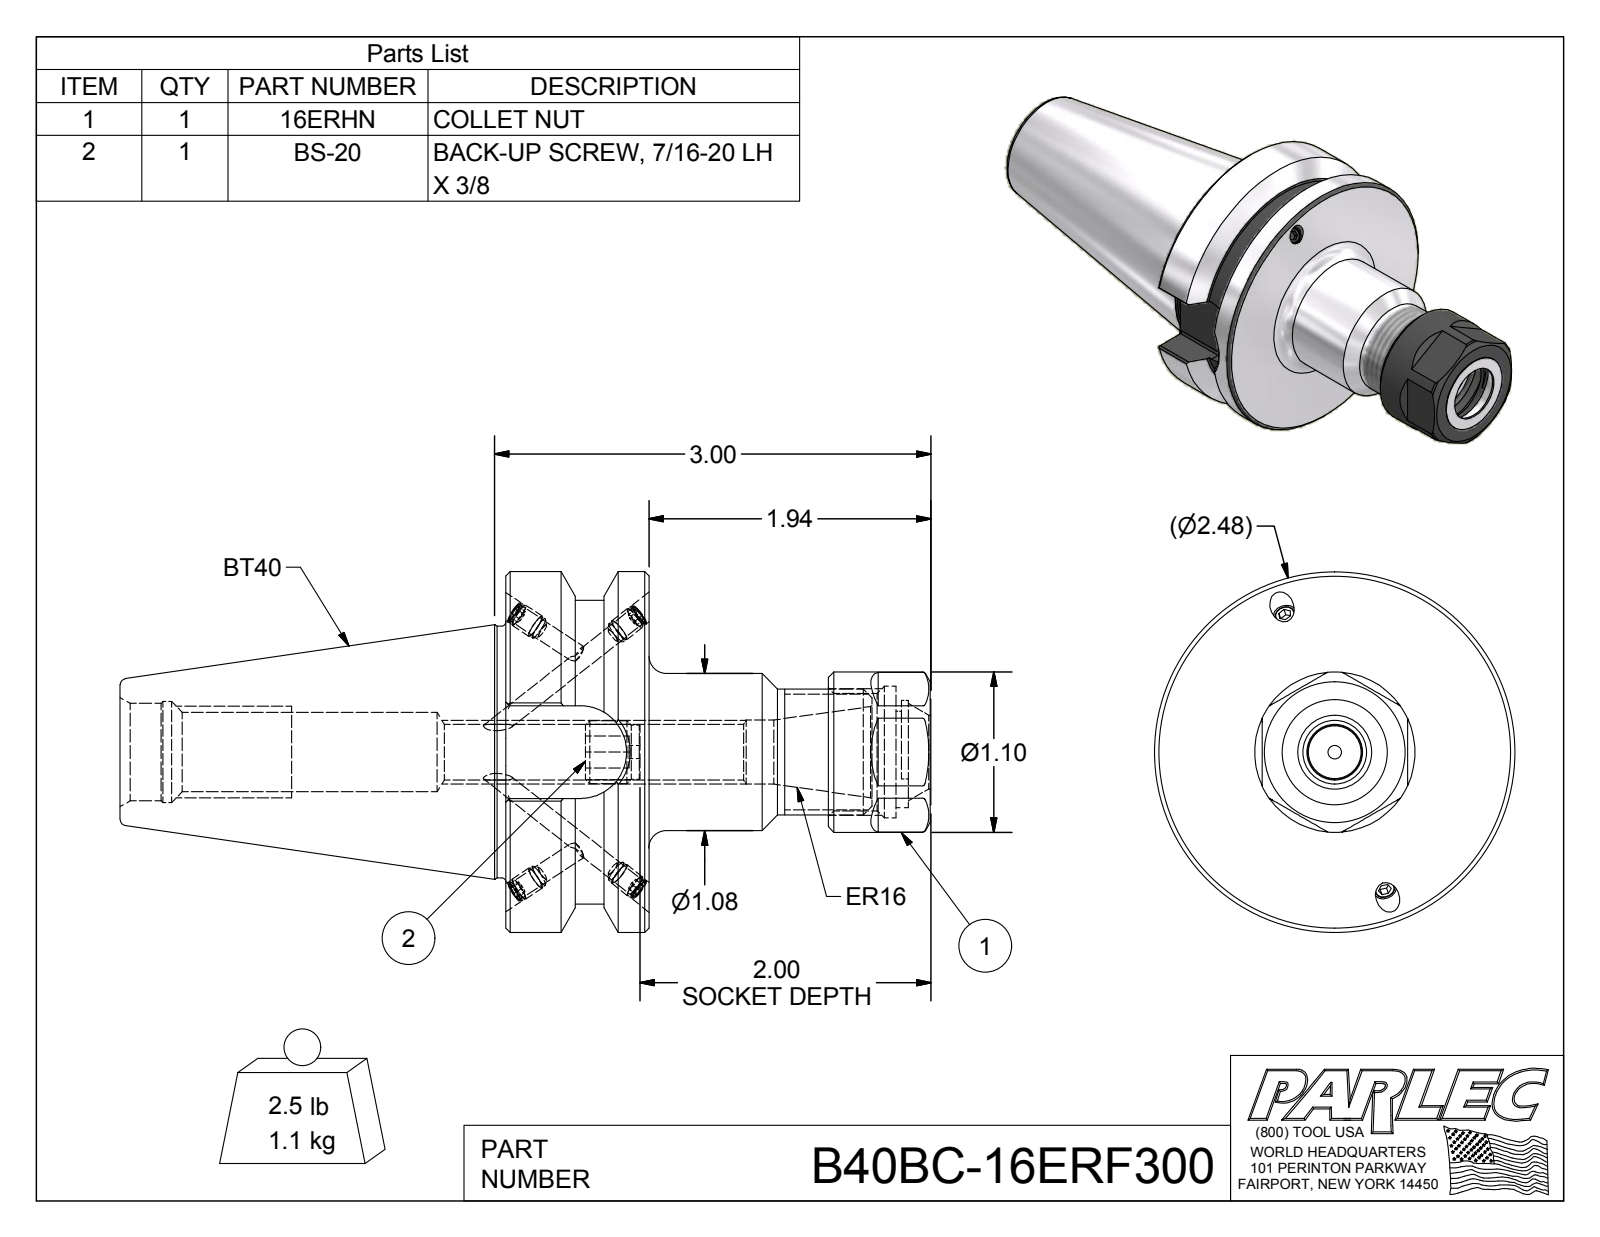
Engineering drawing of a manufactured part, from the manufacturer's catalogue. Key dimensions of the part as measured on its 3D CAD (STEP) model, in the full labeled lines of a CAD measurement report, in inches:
Part name (STEP PRODUCT): B40BCB-16ER3-1; 029-965; 16ERHN; BS-20 (+1 more)
STEP written by: Autodesk Inventor 2016 (AUTOMOTIVE_DESIGN)
Units: inches
Bodies: 7 solids, 201 faces (93 planar, 53 cylindrical, 55 other)
Overall size (bounding box): 5.575 × 2.48 × 2.48
Volume: 8.666 in³ · Surface area: 48.95 in²
Round holes (diameter × count): ⌀0.13 ×4, ⌀0.161 ×4, ⌀0.09 ×1, ⌀0.383 ×1, ⌀0.44 ×1, ⌀0.488 ×1, ⌀0.545 ×1, ⌀0.67 ×1, ⌀0.67 ×1, ⌀0.694 ×1, ⌀0.807 ×1, ⌀0.906 ×1
Round bosses / shafts (diameter × count): ⌀0.165 ×4, ⌀0.157 ×4, ⌀2.48 ×1, ⌀2.087 ×1, ⌀1.73 ×1, ⌀1.102 ×1, ⌀1.08 ×1, ⌀0.866 ×1
Partial cylindrical surfaces — rounded edges, fillets, slot ends (radius × count): R0.02 ×8, R0.285 ×1, R0.319 ×1, R0.354 ×1
Main face-to-face distances: 0.984, 2.922, 1.938, 0.99, 1.78, 0.395, 1.385, 2.698, 1.714, 0.224
Hole centre spacings: 0.06
